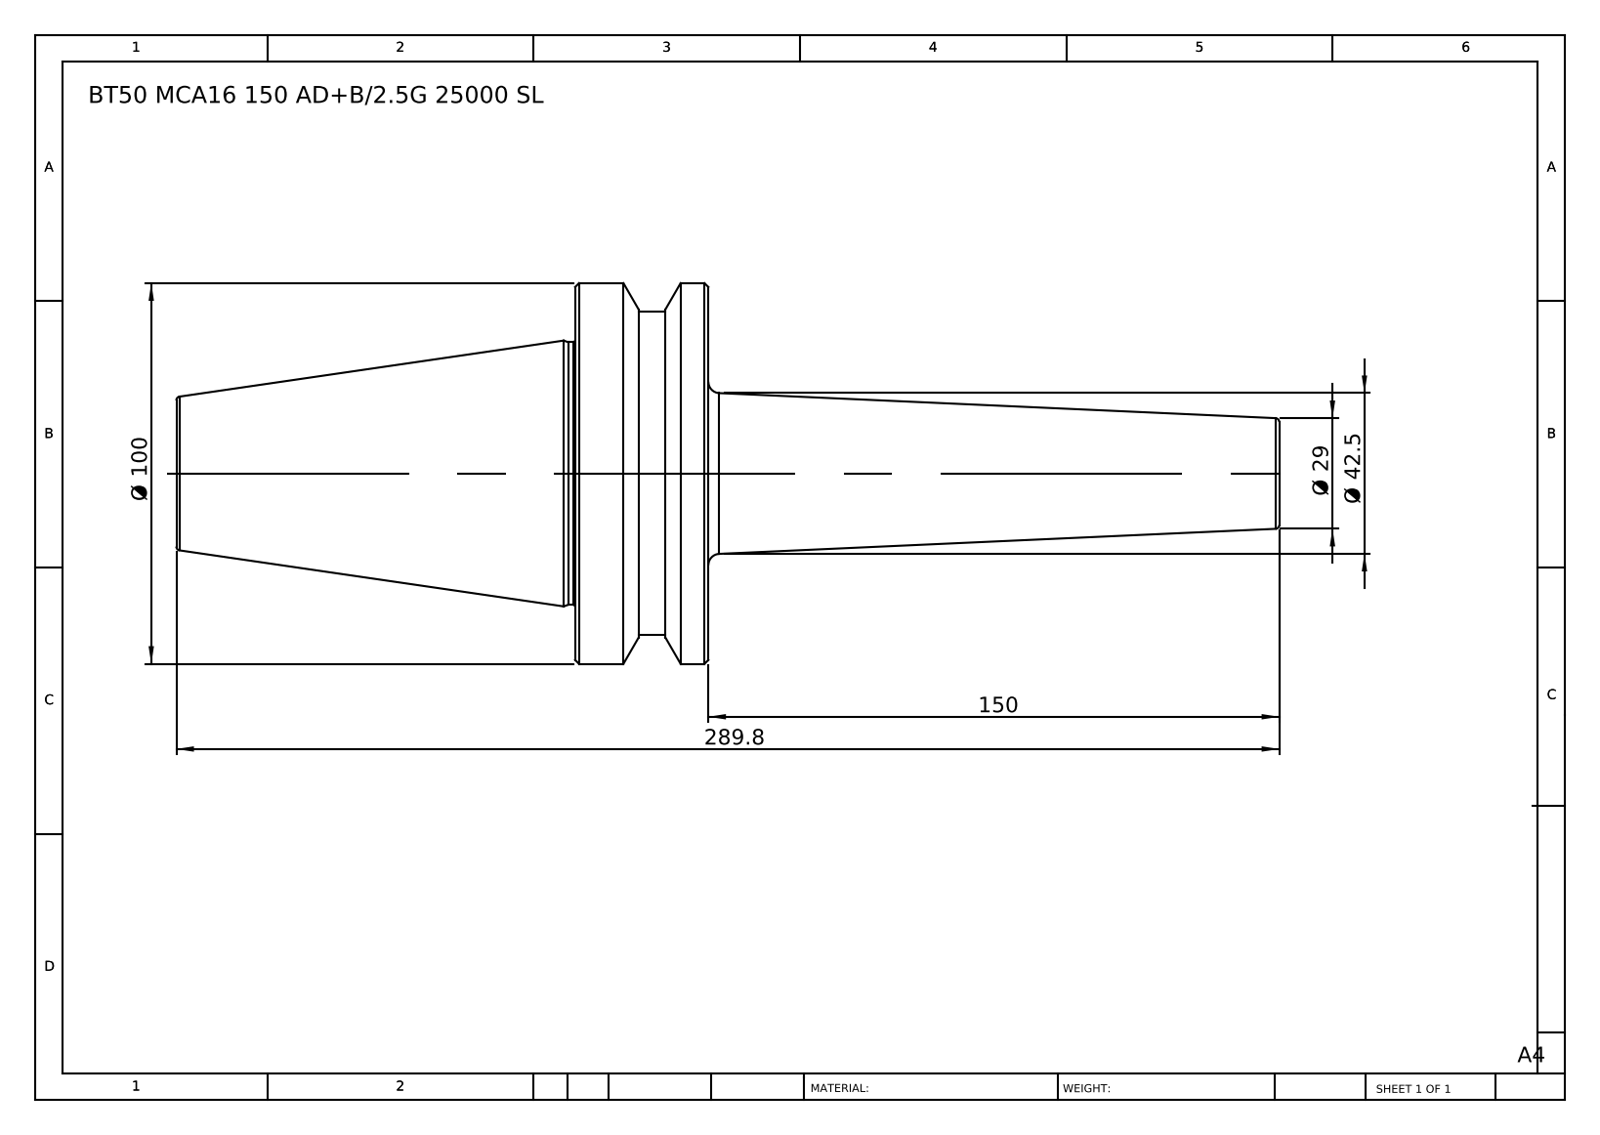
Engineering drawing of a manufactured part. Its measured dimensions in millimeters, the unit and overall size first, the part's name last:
Units: millimetres
Overall size (bounding box): 289.8 × 100 × 100
Round bosses / shafts (diameter × count): ⌀100 ×1, ⌀85 ×1, ⌀69 ×1
Main face-to-face distances: 35, 139.8, 104.8, 150, 185, 289.8, 161.3, 11.3, 23.7, 128.5
Volume: 662 630 mm³ · Surface area: 60 282 mm²
Bodies: 1 solid, 36 faces (6 planar, 8 cylindrical, 22 other)
Part name (STEP PRODUCT): BT50 MCA16 150 AD+B-2.5G 25000 SL
STEP written by: SolidWorks 2014 (CONFIG_CONTROL_DESIGN)
